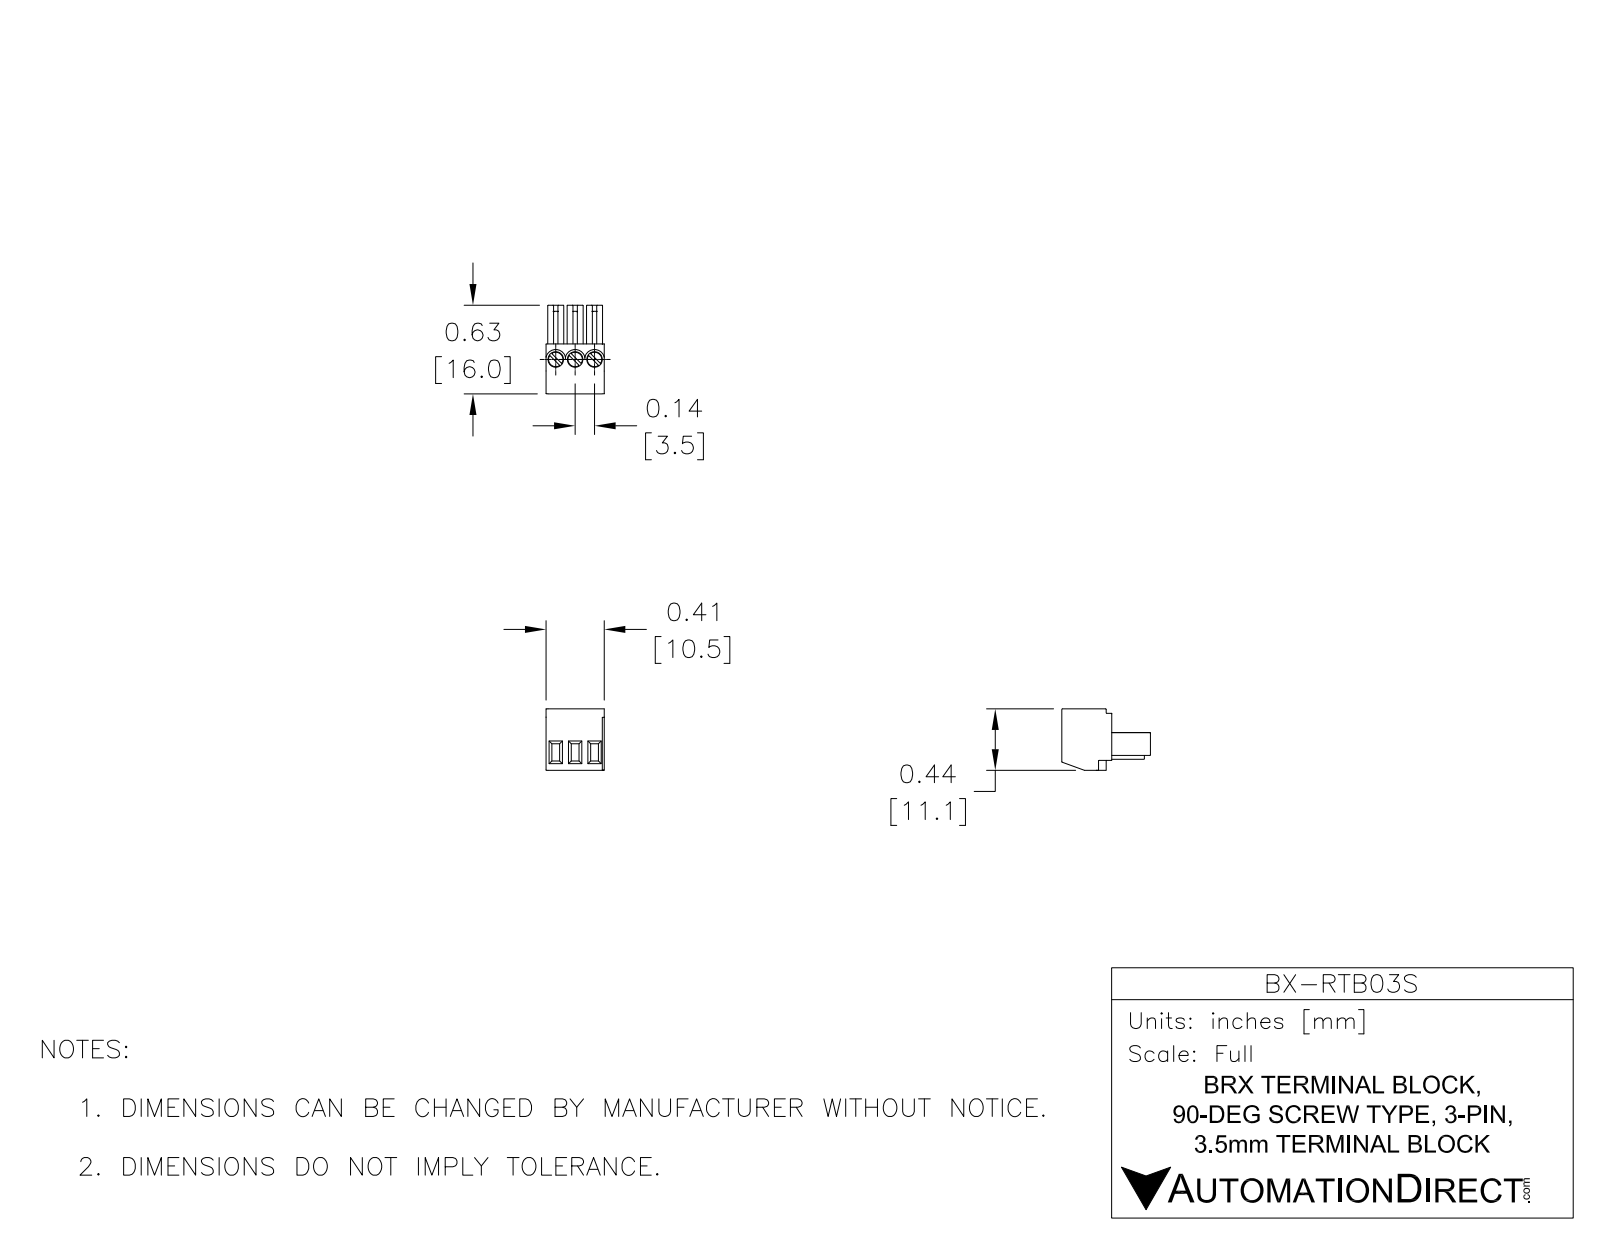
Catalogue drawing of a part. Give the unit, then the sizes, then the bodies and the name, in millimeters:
Units: millimetres
Overall size (bounding box): 16 × 11.1 × 10.5
Round holes (diameter × count): ⌀1 ×3, ⌀2 ×3, ⌀2.8 ×3
Round bosses / shafts (diameter × count): ⌀2.6 ×3
Partial cylindrical surfaces — rounded edges, fillets, slot ends (radius × count): R0.1 ×50, R0.3 ×6, R1.8 ×3, R1.83 ×3
Main face-to-face distances: 3.5, 10.5, 7, 2.91, 9, 0.59, 6.41, 8.4, 3.2, 3.8
Hole centre spacings: 3.5, 7
Volume: 1 175 mm³ · Surface area: 1 069 mm²
Bodies: 1 solid, 251 faces (108 planar, 113 cylindrical, 30 other)
Part name (STEP PRODUCT): BX-RTB03S
STEP written by: SolidWorks 2016 (AUTOMOTIVE_DESIGN)
